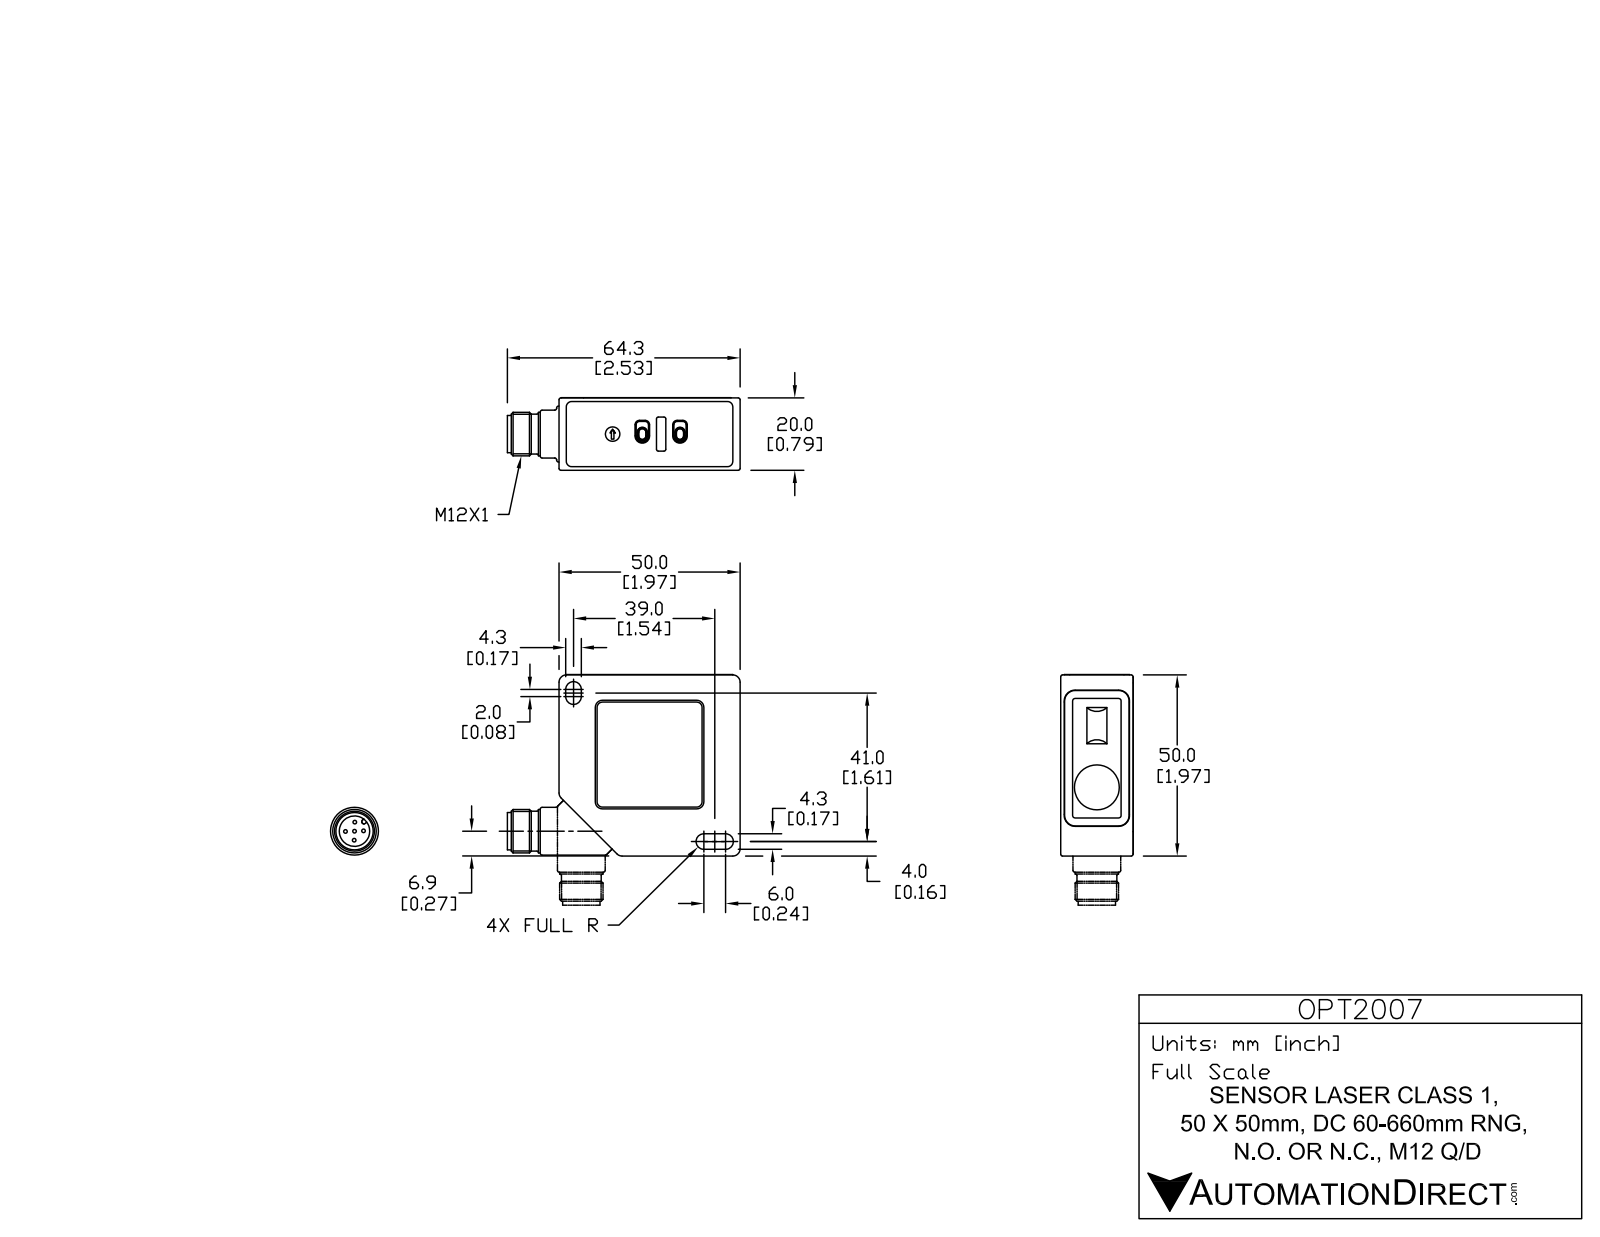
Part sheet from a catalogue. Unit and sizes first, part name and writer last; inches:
Units: inches
Overall size (bounding box): 2.537 × 1.972 × 0.787
Round holes (diameter × count): ⌀0.157 ×1, ⌀0.333 ×1
Round bosses / shafts (diameter × count): ⌀0.04 ×5, ⌀0.709 ×1, ⌀0.531 ×1, ⌀0.488 ×1, ⌀0.472 ×1, ⌀0.433 ×1, ⌀0.406 ×1
Partial cylindrical surfaces — rounded edges, fillets, slot ends (radius × count): R0.079 ×17, R0.008 ×10, R0.039 ×8, R0.083 ×5, R0.02 ×4, R0.047 ×4, R0.085 ×4, R0.114 ×4
Main face-to-face distances: 0.787, 0.78, 1.969, 1.972, 1.902, 0.063, 1.906, 0.21, 2.111, 2.115
Volume: 2.969 in³ · Surface area: 24.79 in²
Bodies: 12 solids, 289 faces (147 planar, 128 cylindrical, 14 other)
Part name (STEP PRODUCT): OPT2007
STEP written by: SolidWorks 2013 (AUTOMOTIVE_DESIGN)
